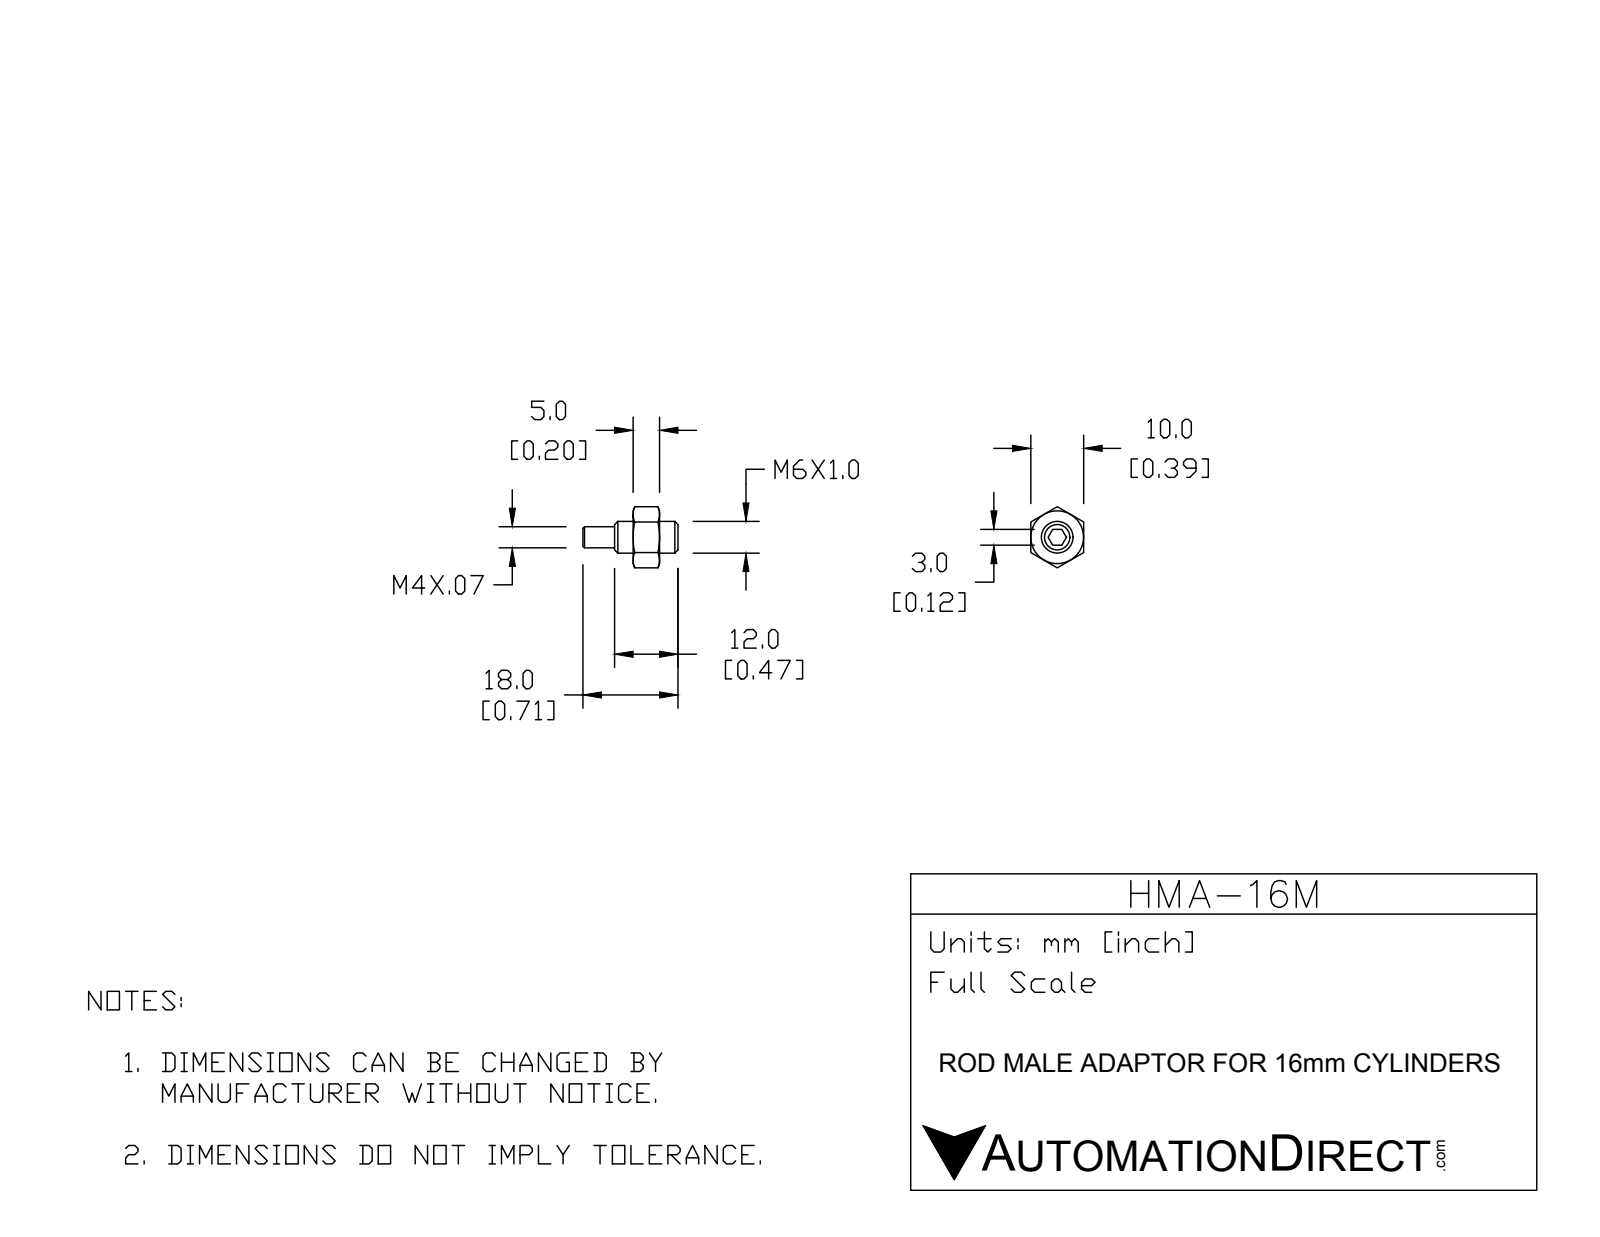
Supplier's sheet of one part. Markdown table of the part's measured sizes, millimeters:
| quantity | value |
| --- | --- |
| part name | HMA-16M |
| STEP written by | SolidWorks 2015 (CONFIG_CONTROL_DESIGN) |
| units | millimeters |
| bodies | 2 solids, 44 faces (18 planar, 6 cylindrical, 20 other) |
| overall size | 18 × 11.55 × 10 |
| volume | 674 mm³ |
| surface area | 751 mm² |
| round holes (diameter × count) | 6 × 1 |
| round bosses / shafts (diameter × count) | 4 × 1 |
| main face-to-face distances | 10, 5, 3, 3.5, 8.5, 18, 14.5, 9.5, 0.5, 5.5 |
